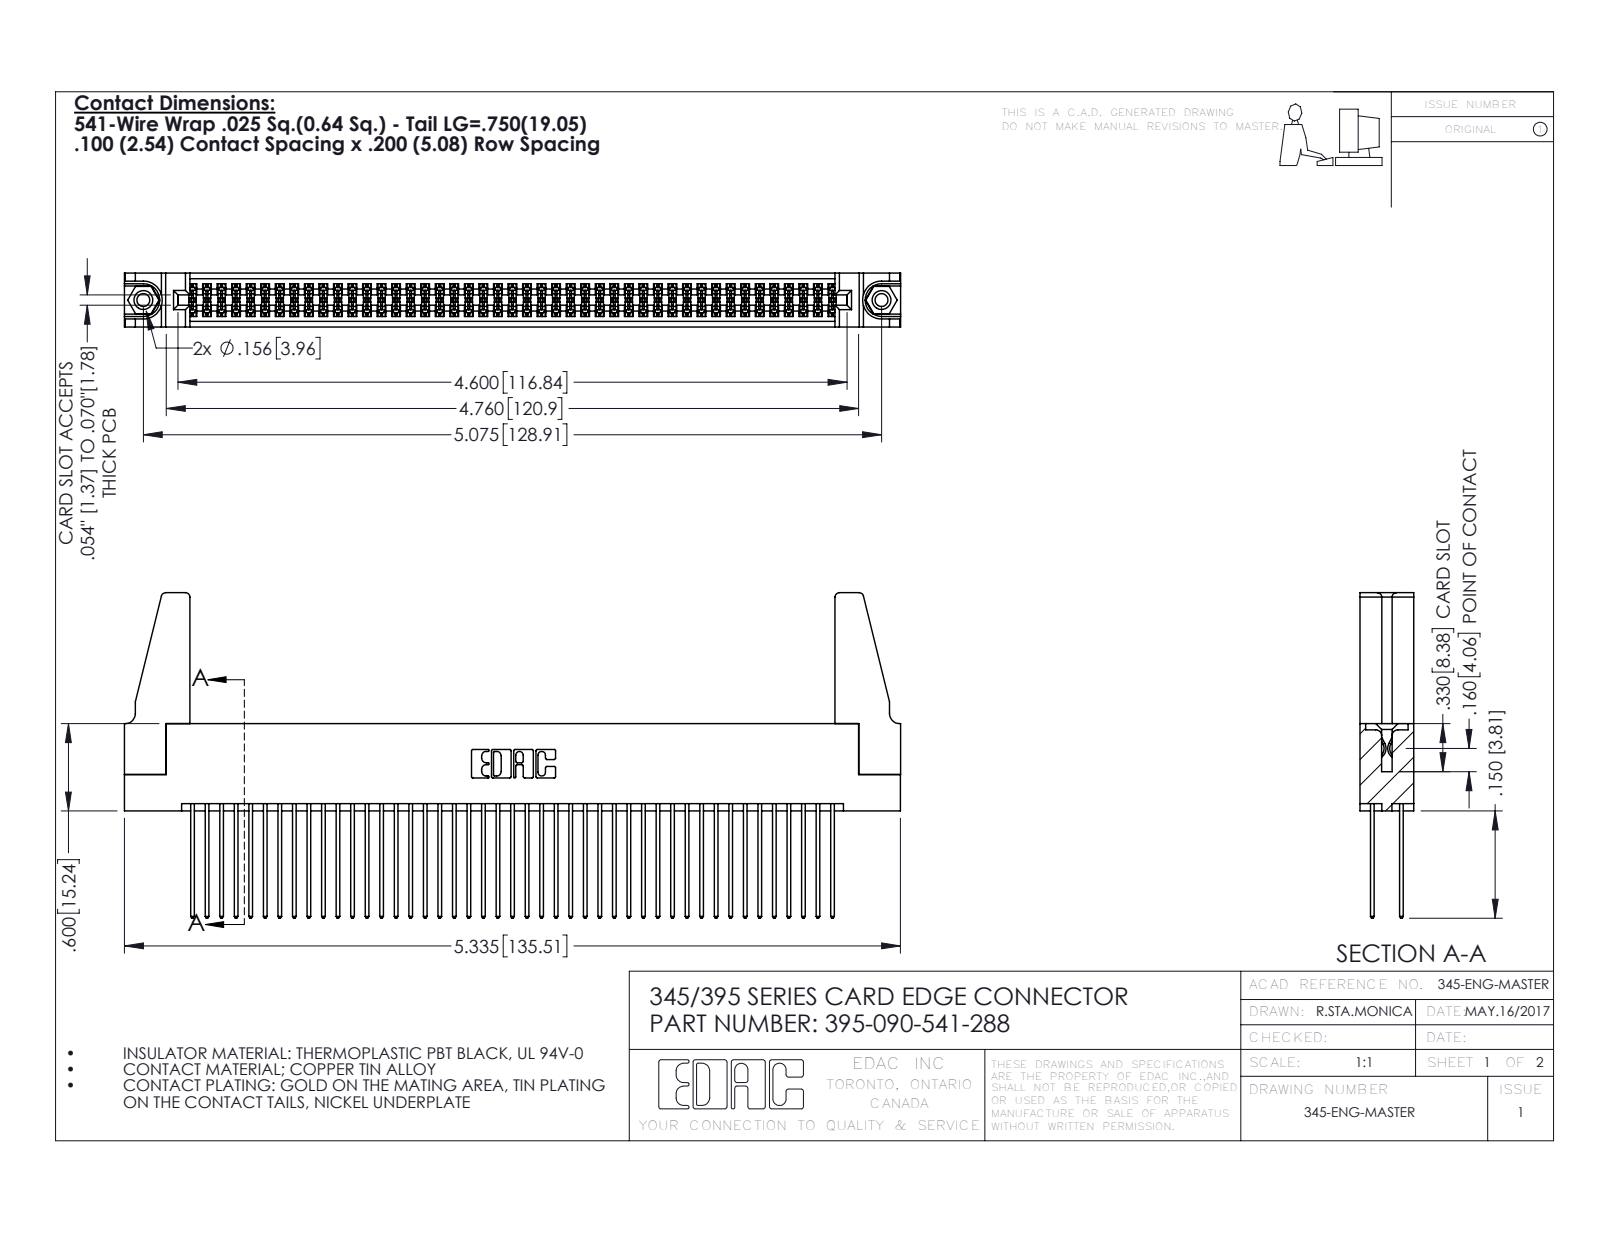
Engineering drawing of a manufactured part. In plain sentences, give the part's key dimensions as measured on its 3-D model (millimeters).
The part is named "395-090-541-288; 345 Part_Flush Mounting Lugs - 0.156 Dia-TH; 345-220-078_345-220-088; 345-250-001_345-250-001-102 (+1 more)". Its 3-D file was written by "SolidWorks 2016 (CONFIG_CONTROL_DESIGN)". It is 95 solids with 4750 faces: 3122 planar, 1612 cylindrical and 16 other. Overall it measures 135.5 by 56.8 by 9.4 millimeters. Its volume is 16 960 cubic millimeters and its surface area 25 870 square millimeters. Round holes: 2 of diameter 2.3, 2 of diameter 3.2, 2 of diameter 4, 1 of diameter 1.6. Round bosses or shafts: 2 of diameter 3.9. Partial cylindrical surfaces (rounded edges, fillets, slot ends): 135 of radius 0.2, 90 of radius 0.3, 22 of radius 0.3, 8 of radius 0.8, 6 of radius 0.2, 6 of radius 0.8, 3 of radius 0.7, 2 of radius 0.4. The main face-to-face distances are 1.8, 7.6, 5.1, 2.5, 6.9, 0.6, 9.4, 5.7, 4.4, 3.8. The hole center spacings are 6.9, 122.9, 128.9.
